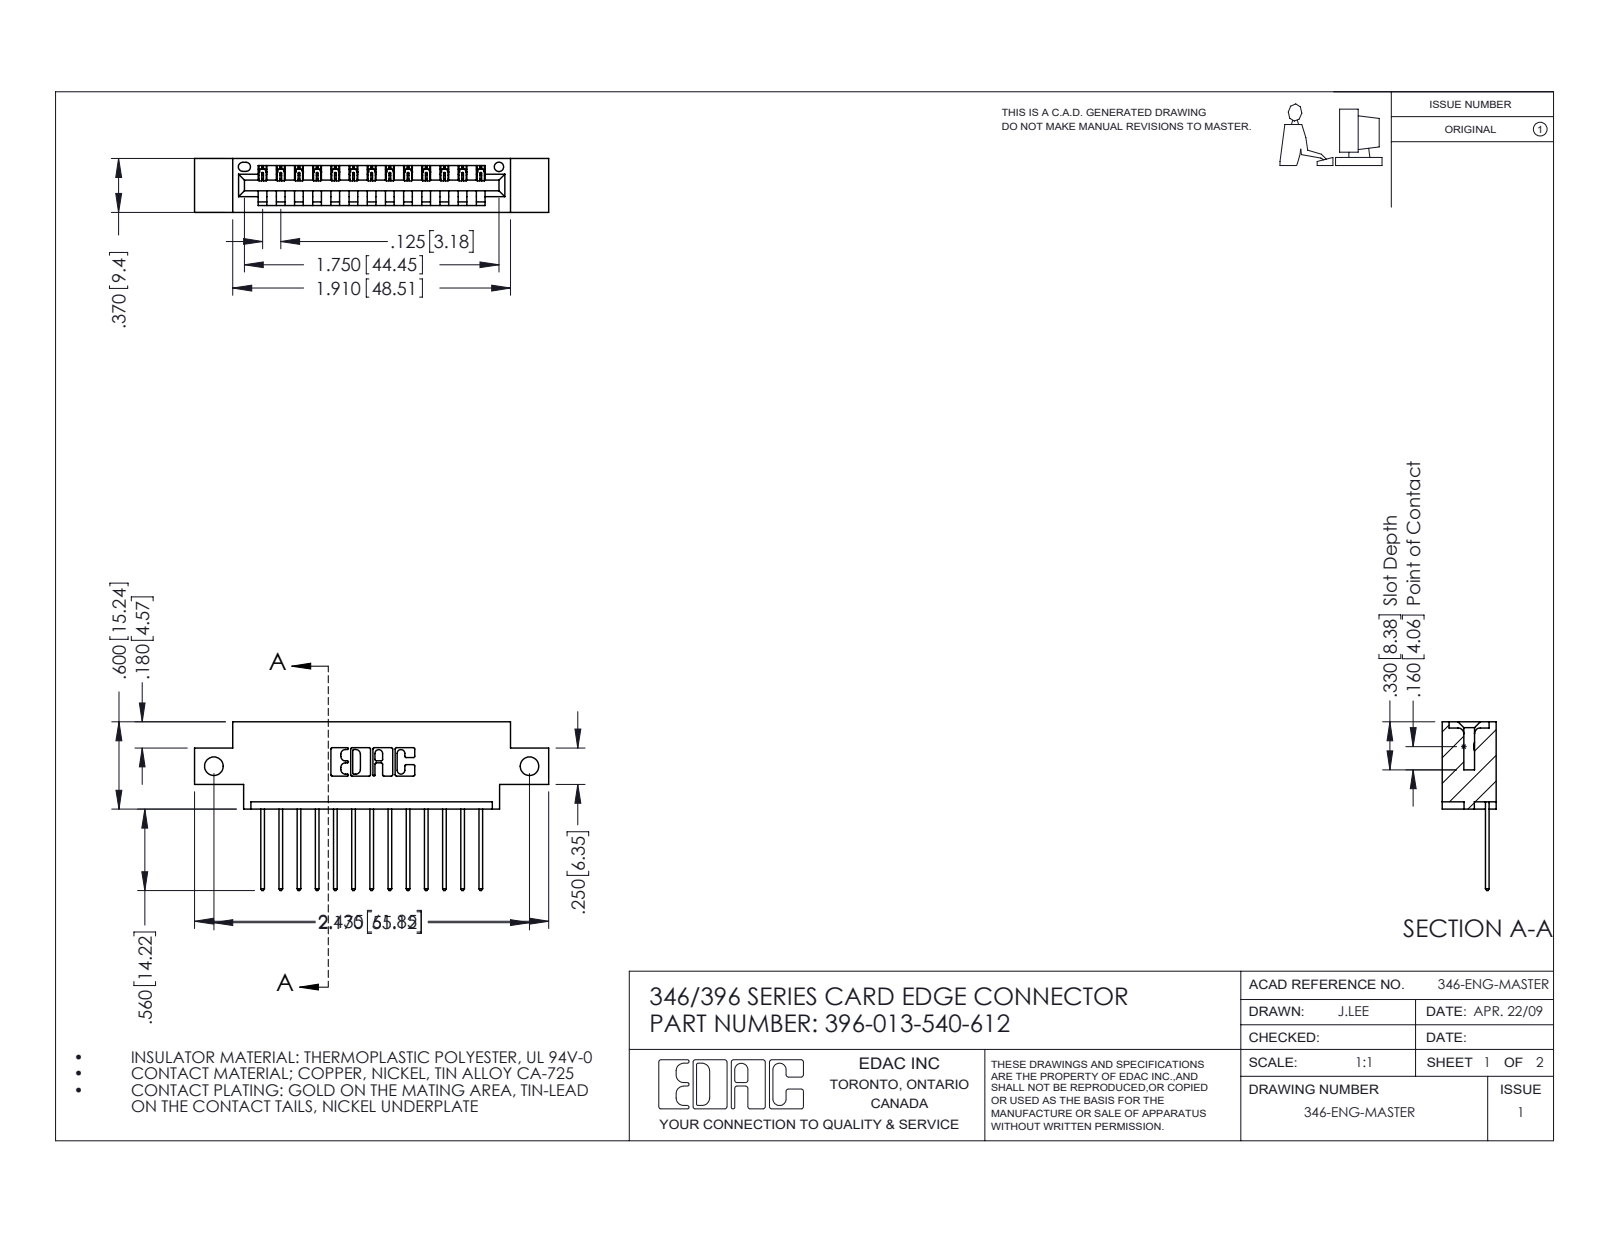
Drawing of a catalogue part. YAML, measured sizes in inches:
part_name: "345-292-001_345-293-140; 396-013-540-612; 346 Part_0.170 Offset - Side Mount"
step_written_by: "SolidWorks 2016 (CONFIG_CONTROL_DESIGN)"
units: inches
bodies: {solids: 14, faces: 880, planar: 600, cylindrical: 280, other: 0}
overall_size: [2.435, 1.16, 0.37]
volume: 0.335
surface_area: 10.38
round_holes:
  - {diameter: 0.128, count: 2}
  - {diameter: 0.064, count: 1}
partial_cylinders:
  - {radius: 0.006, count: 26}
  - {radius: 0.01, count: 26}
  - {radius: 0.01, count: 22}
  - {radius: 0.007, count: 6}
  - {radius: 0.031, count: 6}
  - {radius: 0.026, count: 3}
  - {radius: 0.031, count: 2}
  - {radius: 0.04, count: 2}
face_to_face_distances: [0.25, 0.048, 0.322, 0.37, 0.072, 0.298, 0.025, 0.148, 0.222, 0.1]
hole_center_spacings: [2.17]
